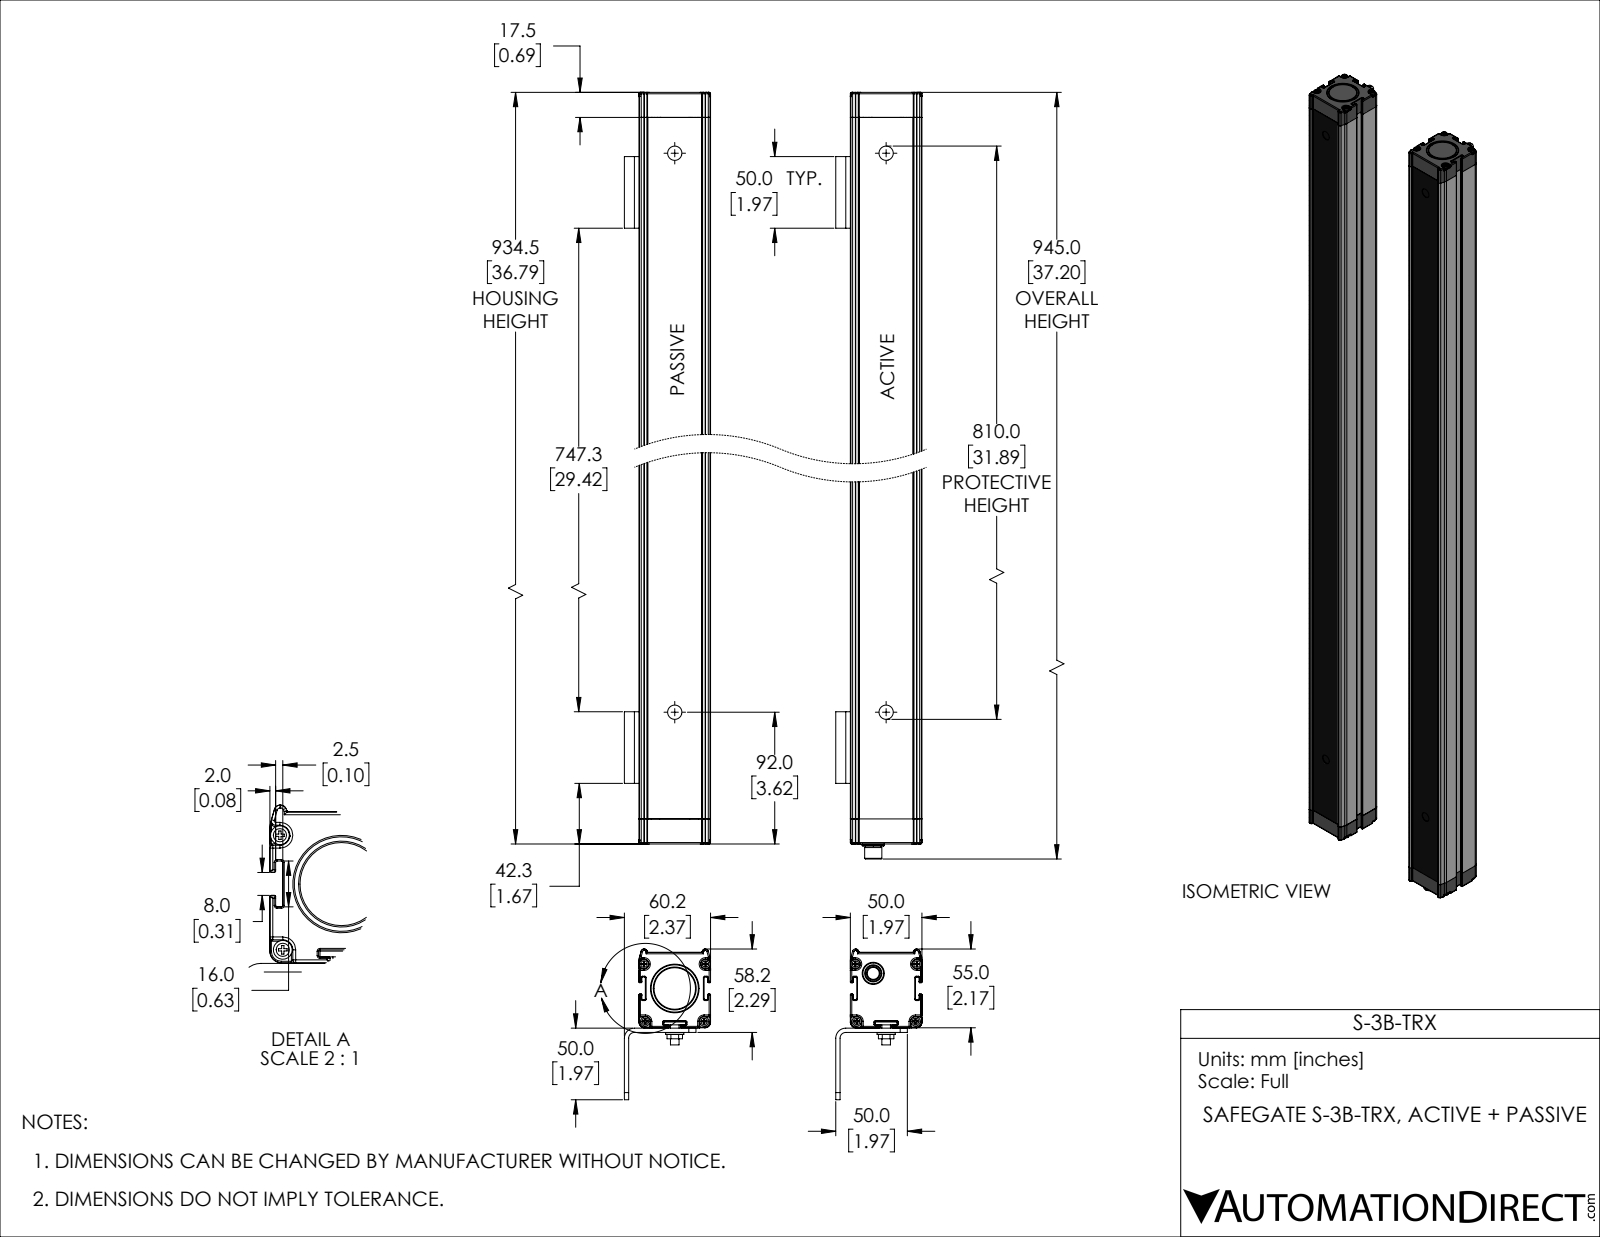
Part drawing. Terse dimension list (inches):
name: S-3B-TRX; S-3B-TRX_1; S-3B-TRX_2
written by: SolidWorks 2019 (AUTOMOTIVE_DESIGN)
unit: in
bodies: 49 solids, 4099 faces (1844 planar, 1529 cylindrical, 726 other)
size: 37.209 × 8.62 × 4.413
volume: 95.94 in³; area: 1 884 in²
holes: 8× ⌀0.138, 8× ⌀0.236, 8× ⌀0.31, 3× ⌀0.472, 3× ⌀0.551, 2× ⌀0.079, 1× ⌀0.378, 1× ⌀0.394
bosses: 10× ⌀0.177, 8× ⌀0.5, 8× ⌀0.26, 4× ⌀0.591, 1× ⌀0.61, 1× ⌀0.472, 1× ⌀0.433
rounds: 425× R0.02, 208× R0.039, 53× R0.012, 32× R0.128, 16× R0.138, 16× R0.197, 14× R0.059, 9× R0.079
face distances: 0.269, 0.098, 6.25, 0.177, 0.276, 1.693, 1.791, 0.079, 0.118, 1.969
hole spacings: 0.406, 1.139, 1.181, 1.575, 2.283, 6.25, 6.256, 6.361
